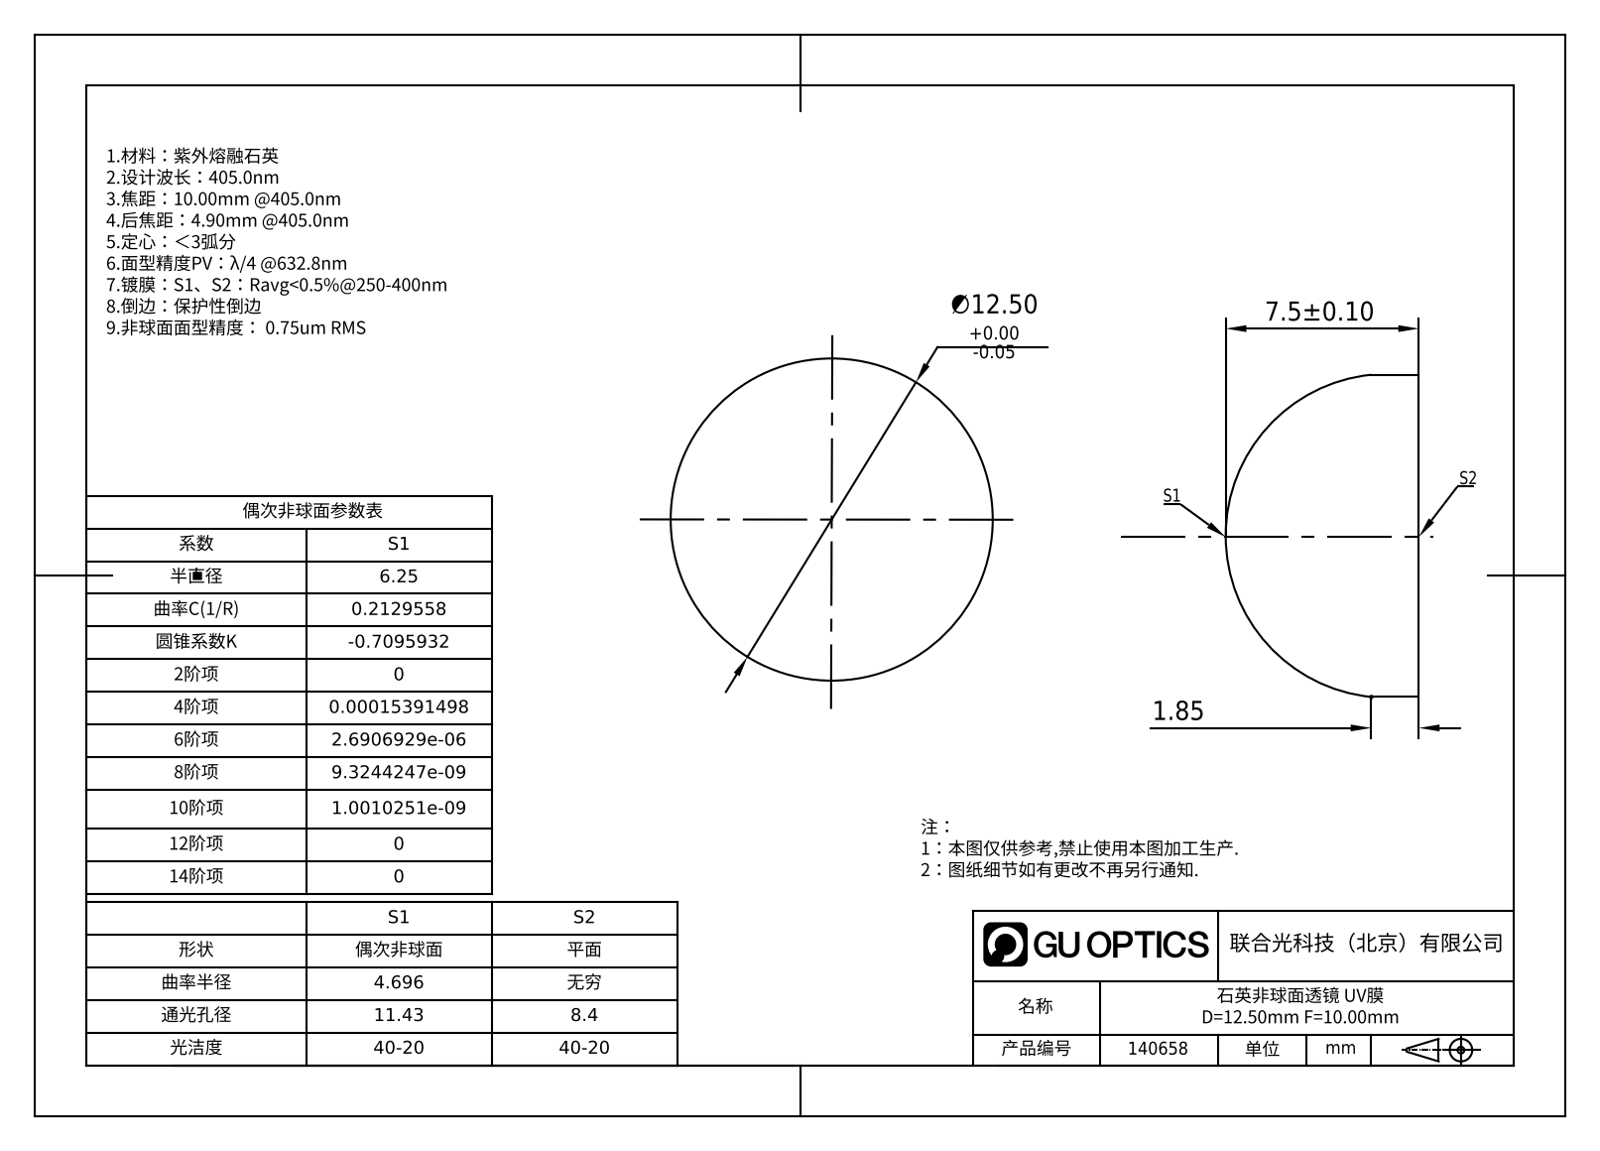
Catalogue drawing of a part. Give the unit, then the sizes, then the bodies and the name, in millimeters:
Units: millimetres
Overall size (bounding box): 12.5 × 12.5 × 7.5
Round bosses / shafts (diameter × count): ⌀12.5 ×1
Volume: 668 mm³ · Surface area: 414 mm²
Bodies: 1 solid, 7 faces (1 planar, 2 cylindrical, 4 other)
Part name (STEP PRODUCT): GLA21-012-010-UV
STEP written by: SolidWorks 2022 (AUTOMOTIVE_DESIGN)
